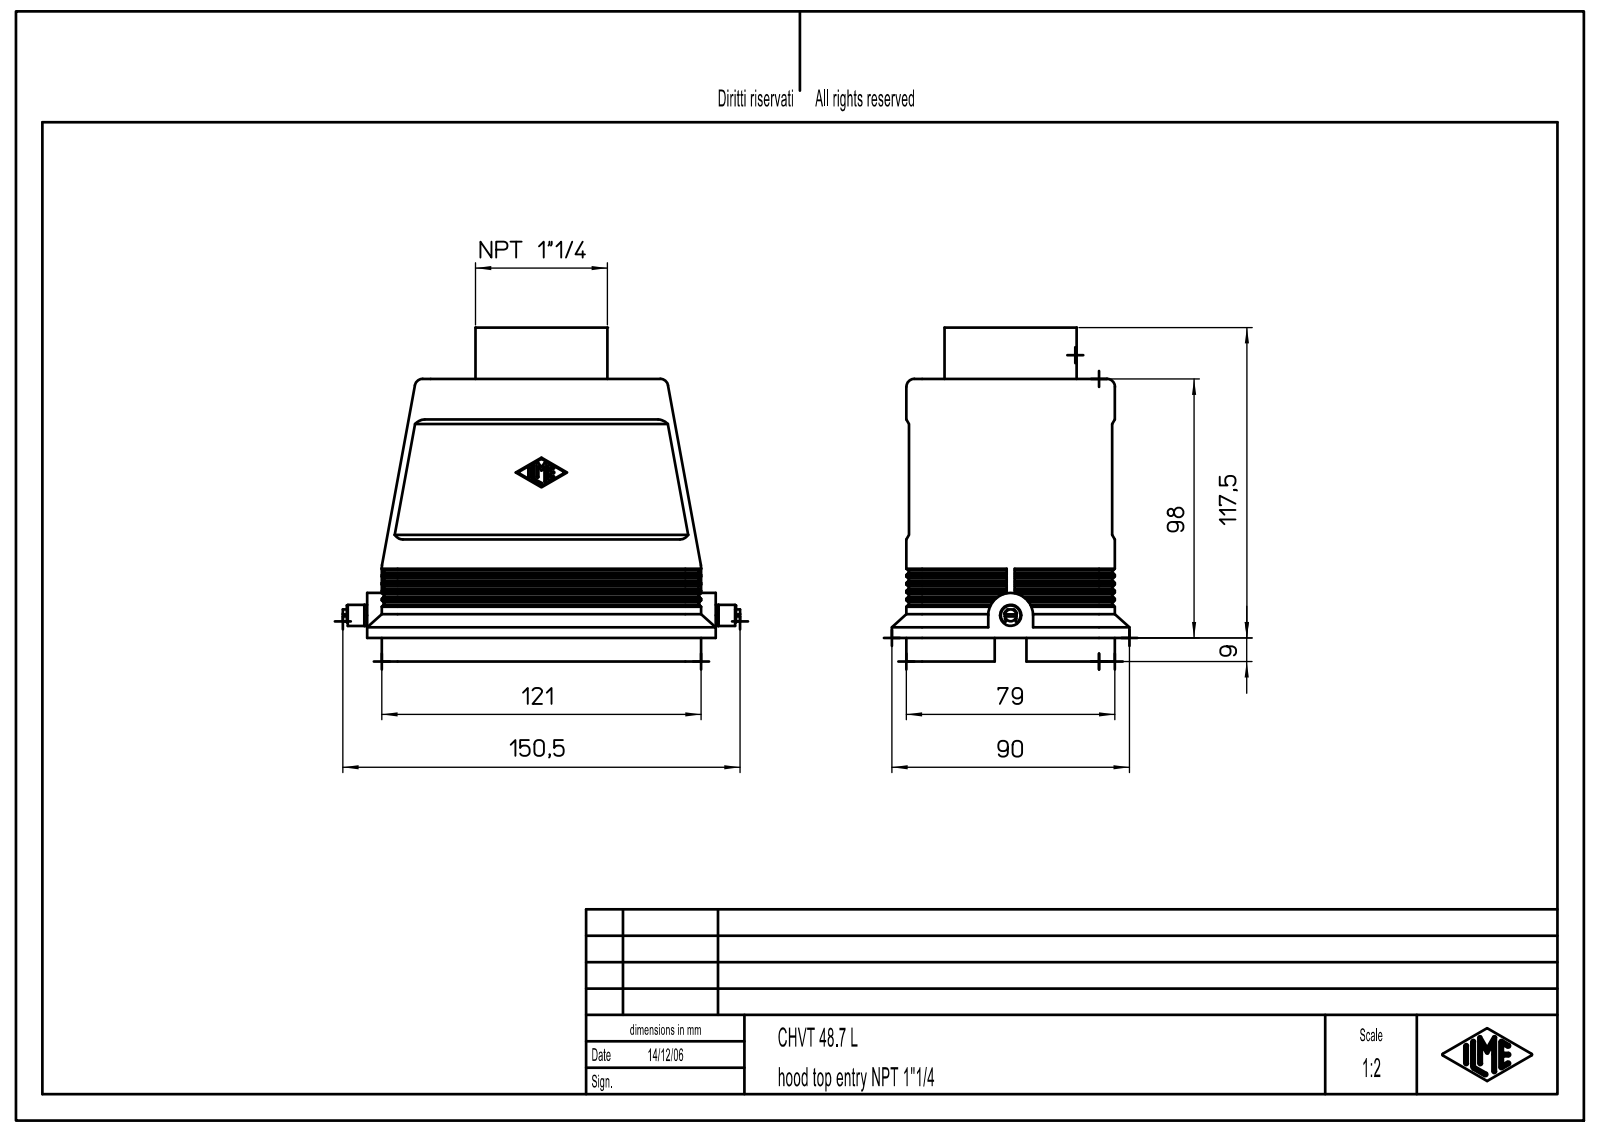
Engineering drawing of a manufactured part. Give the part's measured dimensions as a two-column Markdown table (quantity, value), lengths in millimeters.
| quantity | value |
| --- | --- |
| part name | CHV_48_L; CHV_48_L.stp |
| STEP written by | Creo Elements/Direct Modeling 18.0B 02-Dec-2011 (C) Parametric Technology GmbH (AUTOMOTIVE_DESIGN) |
| units | millimeters |
| bodies | 1 solid, 593 faces (338 planar, 185 cylindrical, 70 other) |
| overall size | 150.5 × 126.5 × 90 |
| volume | 238 347 mm³ |
| surface area | 106 554 mm² |
| round holes (diameter × count) | 2.46 × 8, 3.5 × 8, 48 × 1 |
| round bosses / shafts (diameter × count) | 50 × 1, 45.3 × 1, 8 × 1, 6 × 1, 4.5 × 1, 3.5 × 1 |
| partial cylindrical surfaces (radius × count) | 0.38 × 14, 2 × 12, 6 × 8, 0.5 × 4, 3 × 4, 5 × 4, 11.5 × 4, 0.95 × 3 |
| main face-to-face distances | 2.5, 3.5, 74.5, 72, 1, 75.5, 78, 8.5, 10, 77 |
| hole center spacings | 27, 35, 52.15, 60.54, 104, 107.45, 109.73, 8 |
